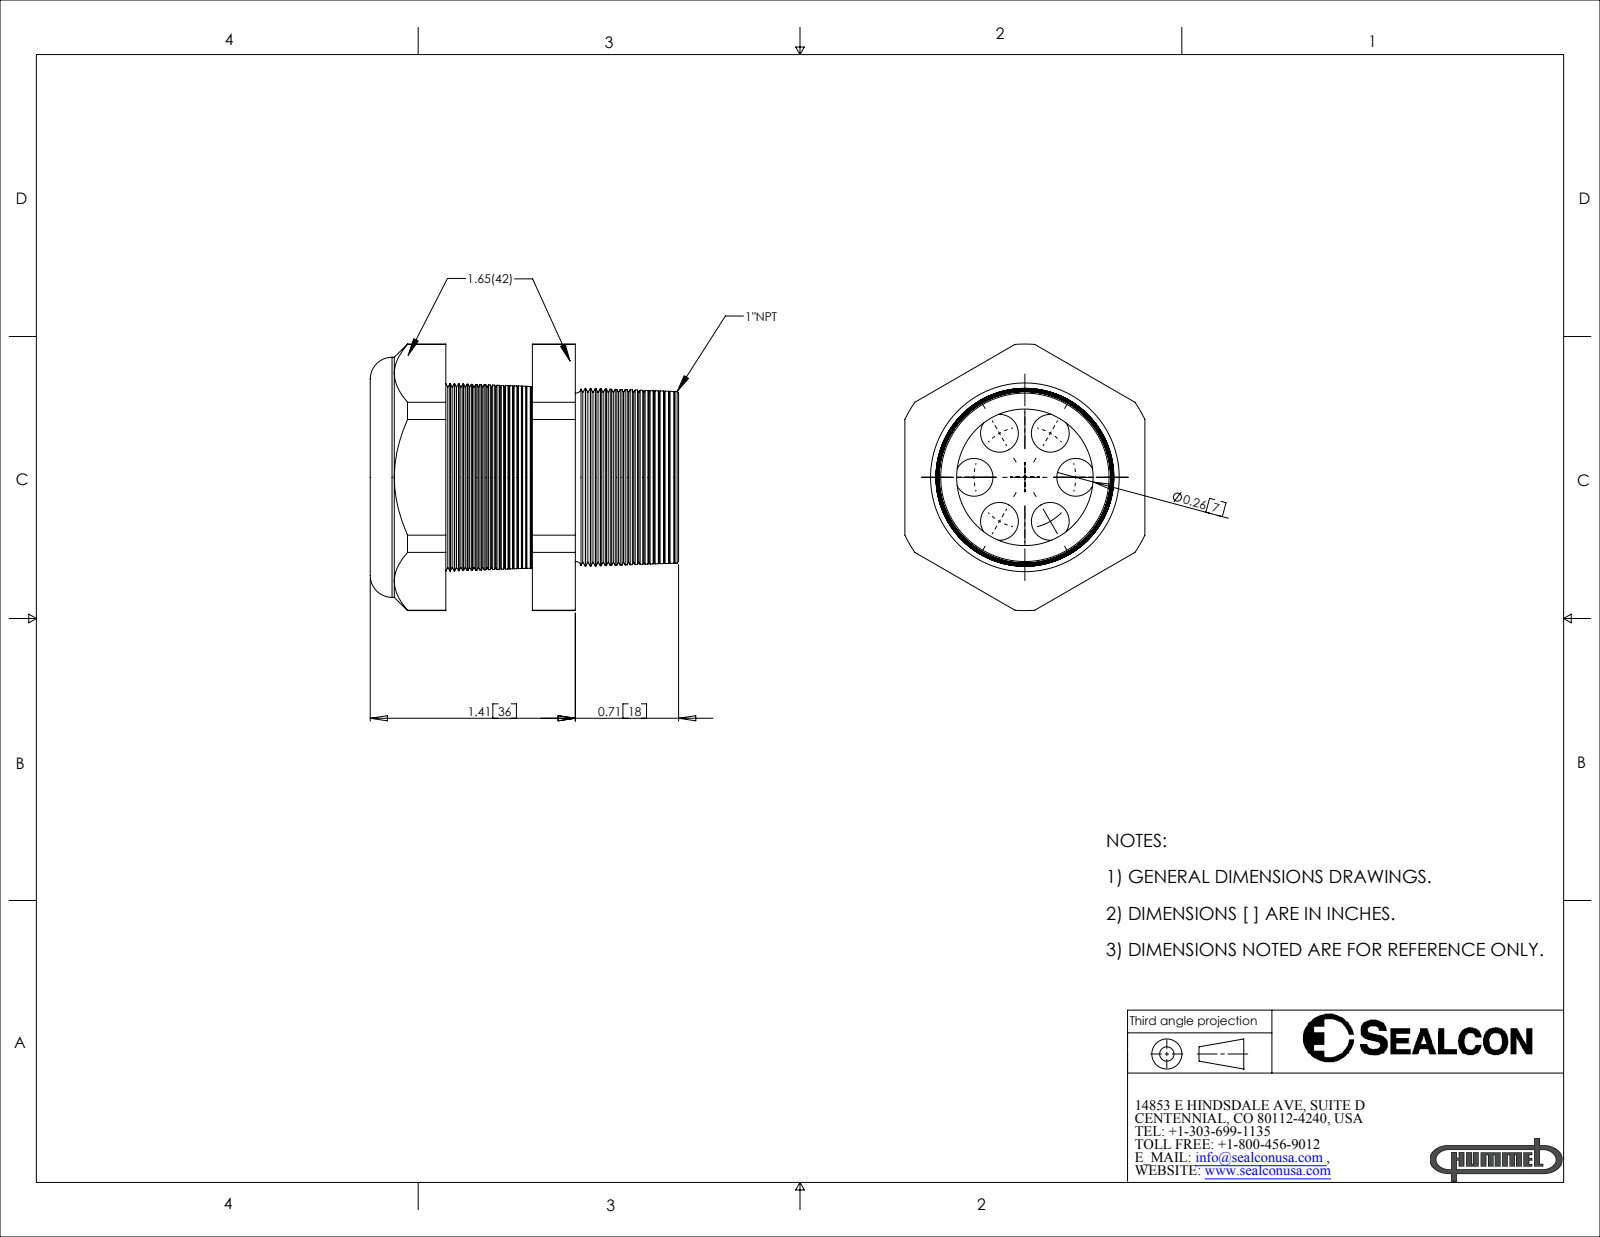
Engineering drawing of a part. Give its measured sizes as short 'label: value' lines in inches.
name: CD29N1-GY
written by: SolidWorks 2007 (CONFIG_CONTROL_DESIGN)
unit: in
bodies: 2 solids, 302 faces (20 planar, 32 cylindrical, 250 other)
size: 2.12 × 1.831 × 1.65
volume: 2.026 in³; area: 28.72 in²
holes: 6× ⌀0.26, 1× ⌀0.96, 1× ⌀0.98
bosses: 1× ⌀1.65
rounds: 1× R0.916
face distances: 0.555, 0.85, 0.295, 1.65, 0.52, 1.075, 1.37, 1.65, 0.5, 0.02
hole spacings: 0.35, 0.606, 0.699
